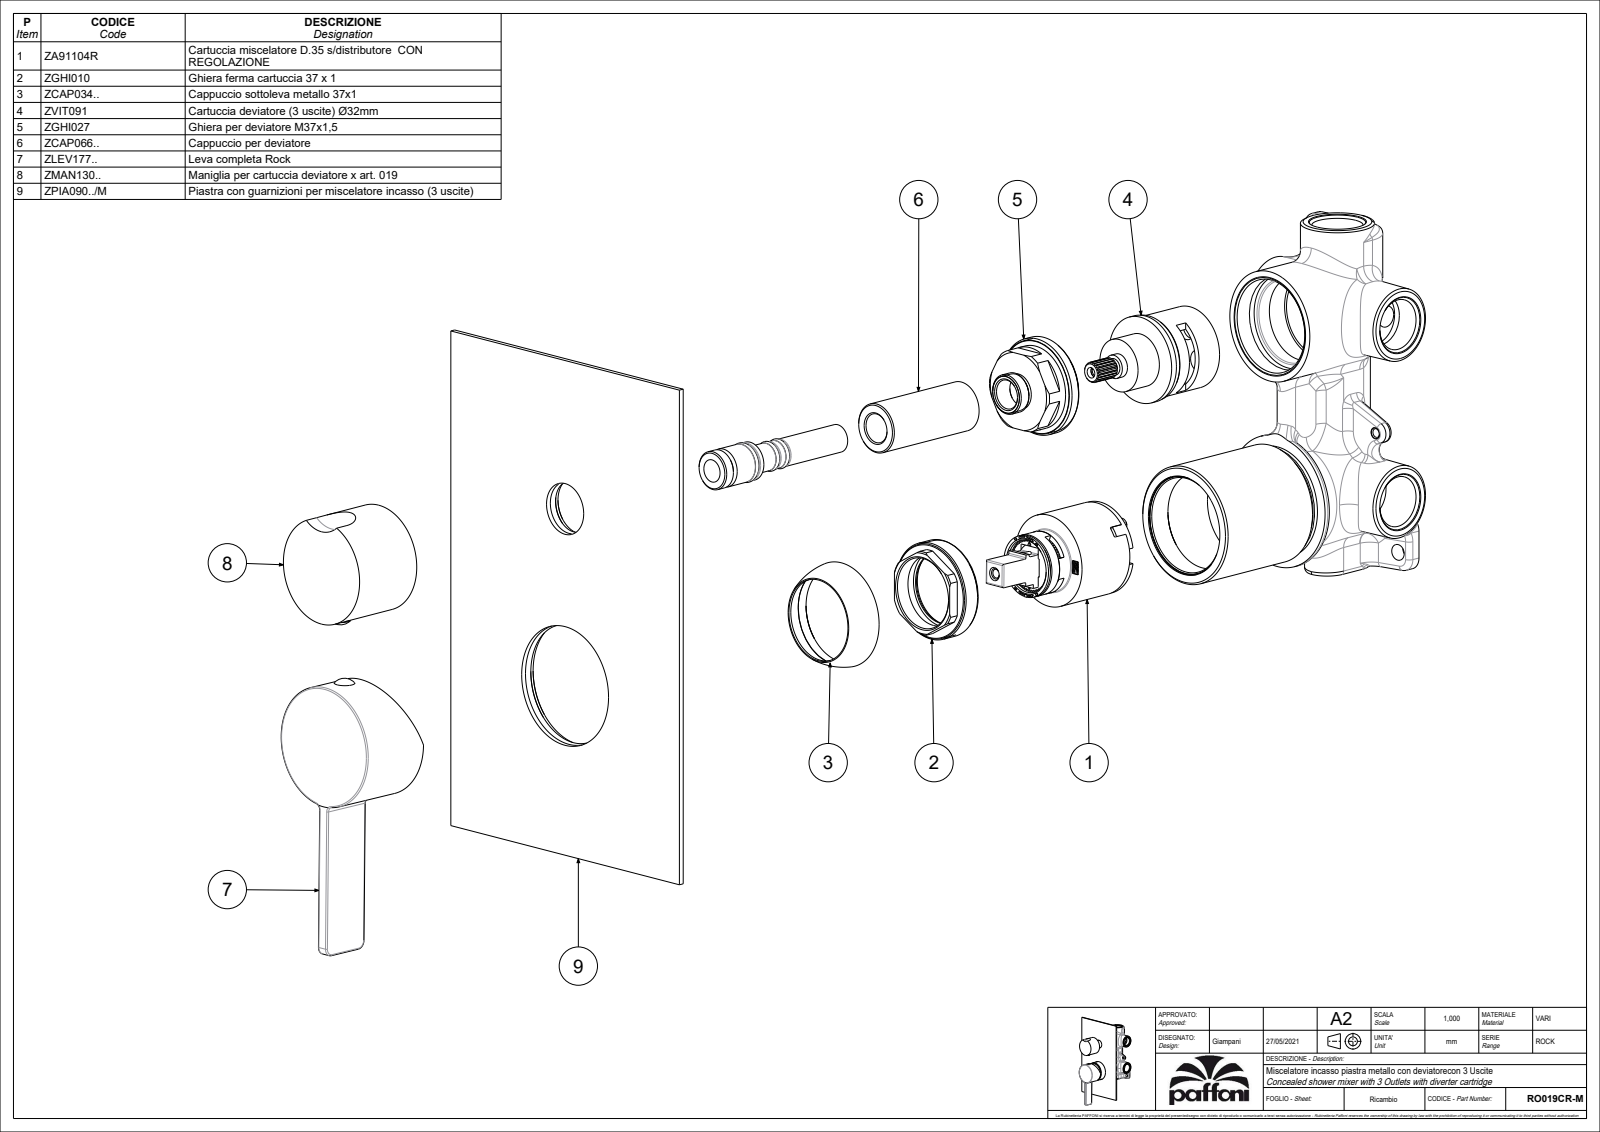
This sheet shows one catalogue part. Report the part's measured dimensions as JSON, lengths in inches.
{"part_name": "RO018CR-M", "step_written_by": "CREO PARAMETRIC BY PTC INC, 2020044 (CONFIG_CONTROL_DESIGN)", "units": "inches", "bodies": {"solids": 0, "faces": 65, "planar": 17, "cylindrical": 21, "other": 27}, "overall_size": [8.071, 4.724, 2.372], "round_bosses_or_shafts": [[1.791, 1], [1.764, 1], [1.575, 1], [0.736, 1], [0.299, 1]], "partial_cylinders_radius": [[0.02, 6], [0.079, 2], [0.118, 2], [0.492, 1]], "face_to_face_distances": [0.079, 1.063, 0.984, 1.177, 1.098, 0.114, 0.177, 2.274, 2.451, 4.724]}
